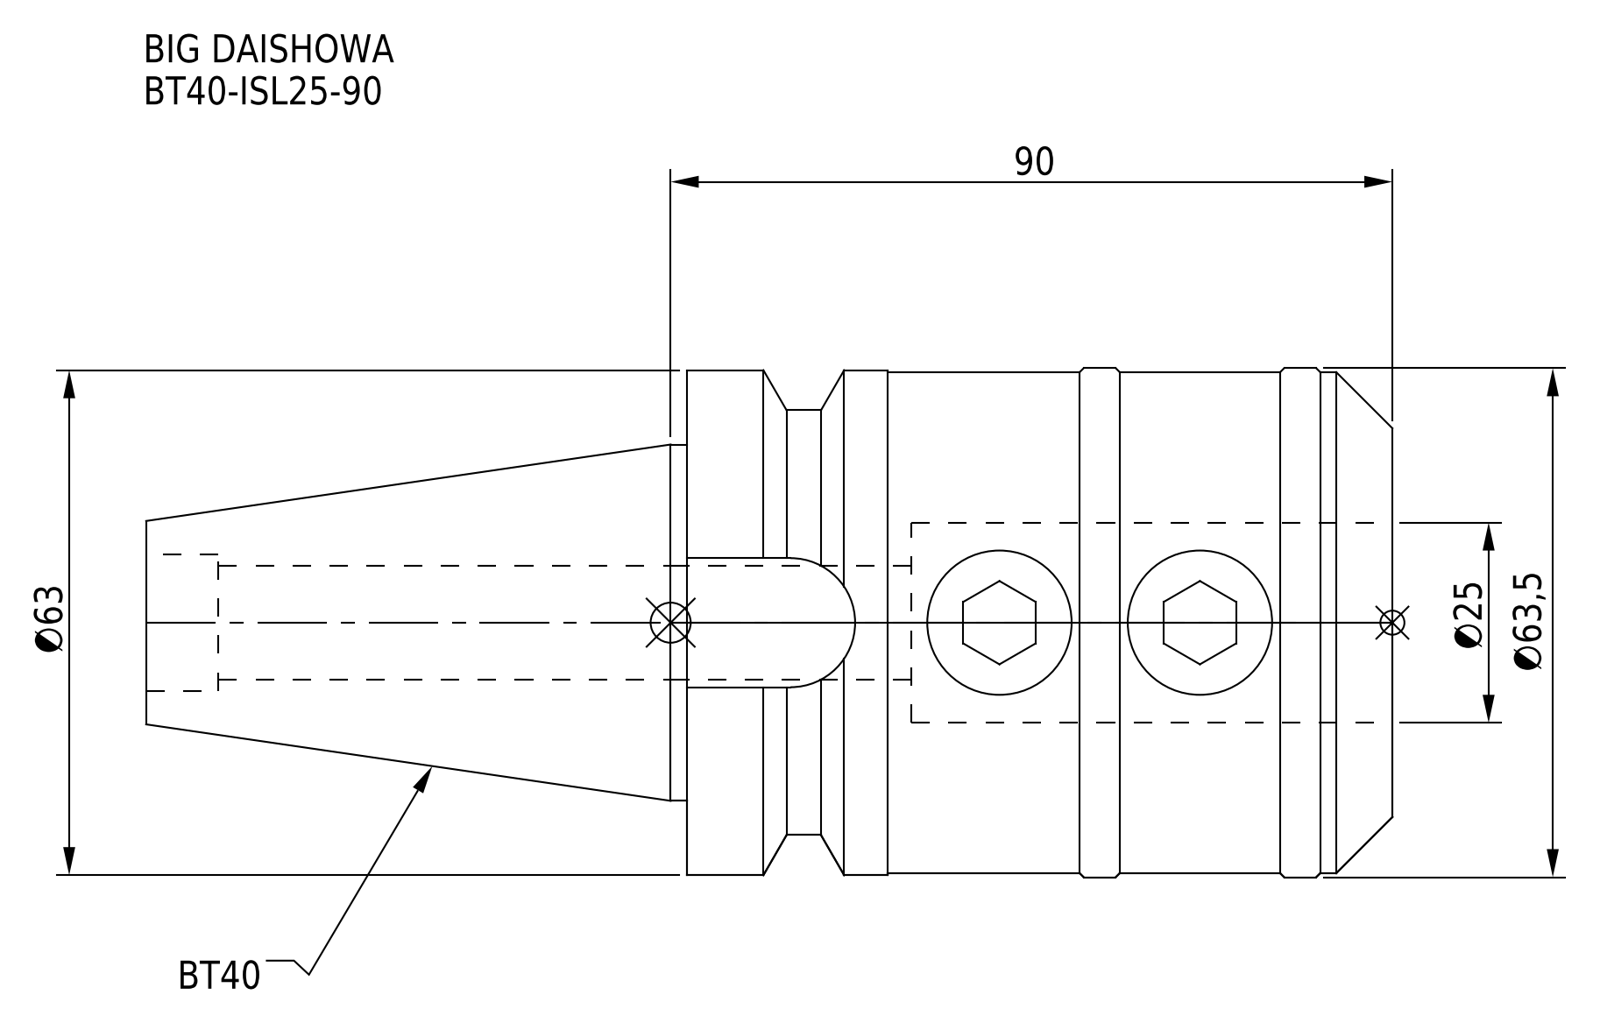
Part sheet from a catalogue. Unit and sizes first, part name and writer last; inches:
Units: inches
Overall size (bounding box): 6.118 × 2.5 × 2.5
Round holes (diameter × count): ⌀0.559 ×1, ⌀0.669 ×1, ⌀0.984 ×1
Round bosses / shafts (diameter × count): ⌀2.5 ×1, ⌀2.48 ×1, ⌀2.461 ×1, ⌀2.087 ×1, ⌀1.75 ×1
Partial cylindrical surfaces — rounded edges, fillets, slot ends (radius × count): R0.317 ×1
Main face-to-face distances: 3.465, 2.362, 1.102, 1.772, 6.118, 3.756, 2.654, 0.634, 5.764, 3.402
Volume: 17.02 in³ · Surface area: 60.68 in²
Bodies: 1 solid, 56 faces (12 planar, 28 cylindrical, 16 other)
Part name (STEP PRODUCT): BT40-ISL25-90
STEP written by: CREO PARAMETRIC BY PTC INC, 2016380 (AUTOMOTIVE_DESIGN)
